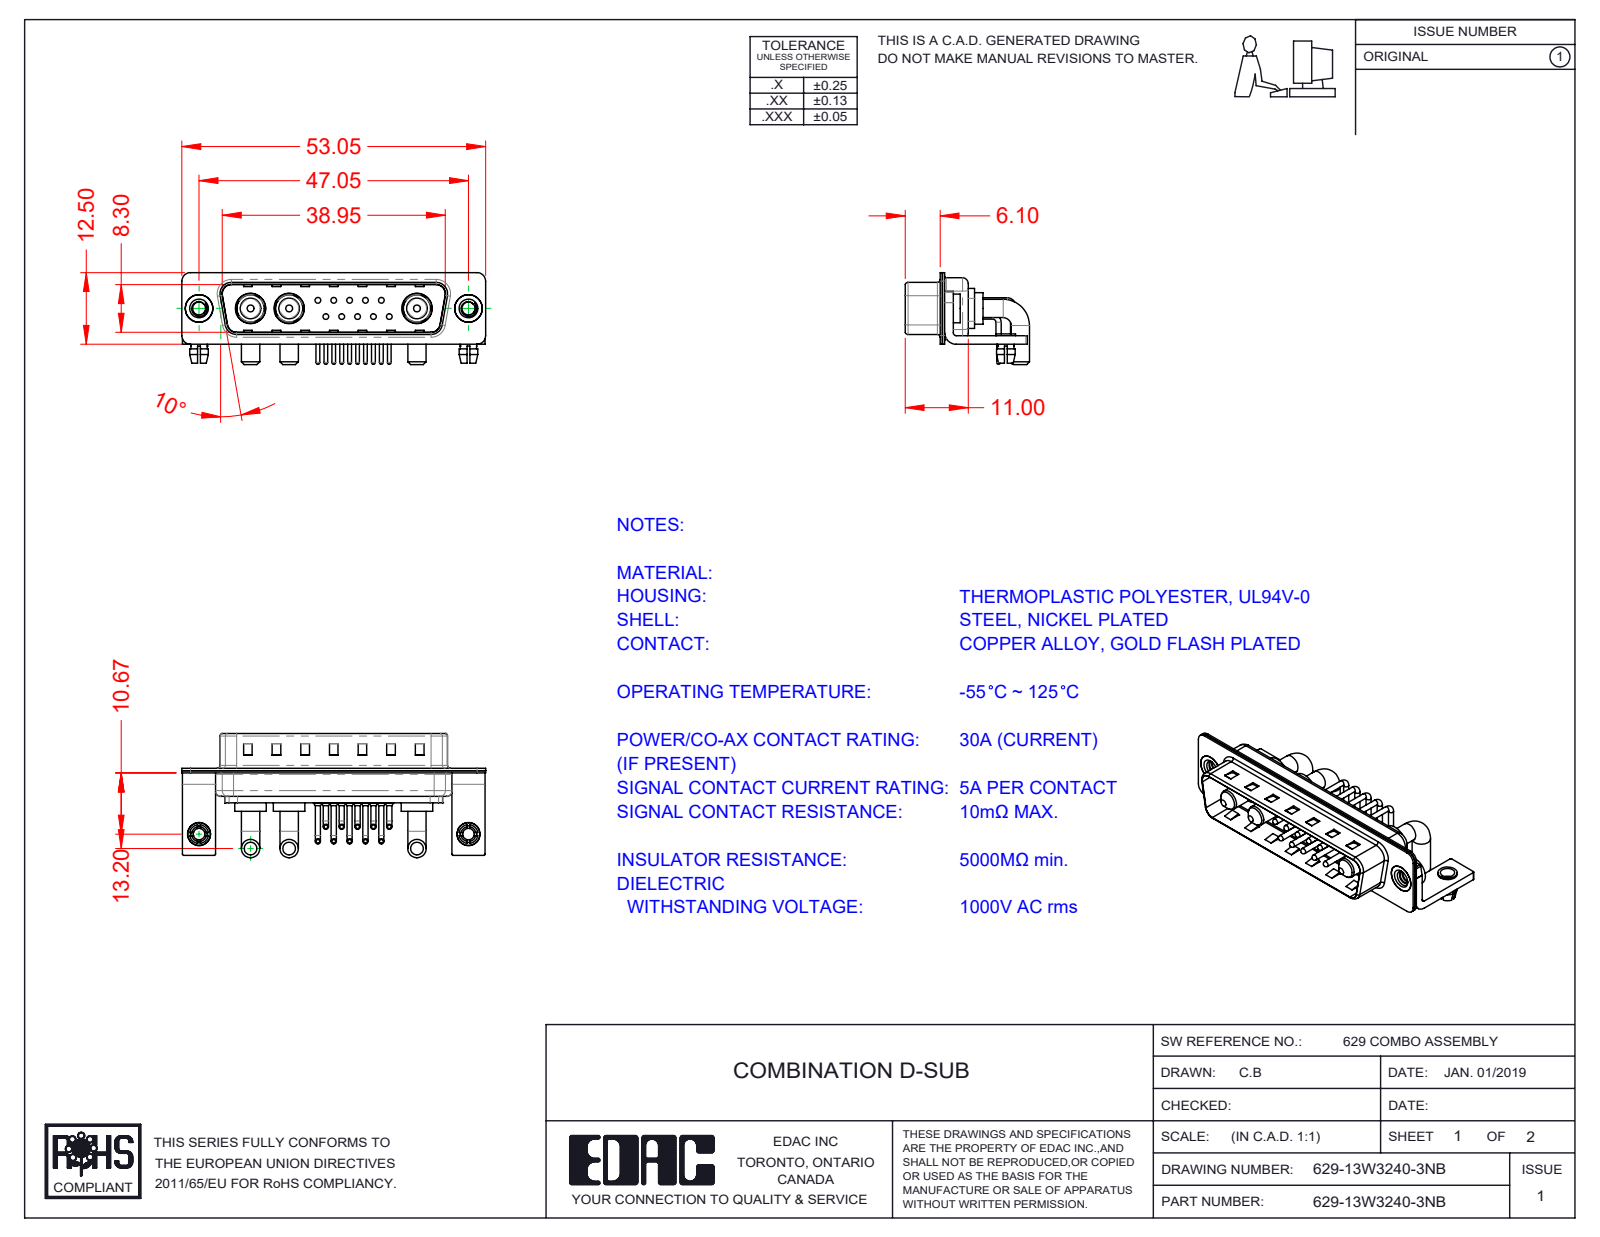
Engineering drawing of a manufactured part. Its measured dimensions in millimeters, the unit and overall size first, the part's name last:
Units: millimetres
Overall size (bounding box): 53.05 × 21.7 × 16.05
Round holes (diameter × count): ⌀2 ×12, ⌀0.75 ×10, ⌀1.6 ×10, ⌀4.85 ×3, ⌀5.3 ×3, ⌀2.26 ×2, ⌀2.5 ×2, ⌀3.2 ×2, ⌀4 ×2, ⌀4.8 ×2
Round bosses / shafts (diameter × count): ⌀0.9 ×20, ⌀1.5 ×10, ⌀1 ×10, ⌀0.65 ×10, ⌀3.2 ×6, ⌀5.5 ×3, ⌀5.2 ×3, ⌀4.75 ×3
Partial cylindrical surfaces — rounded edges, fillets, slot ends (radius × count): R0.25 ×16, R1.5 ×16, R2 ×13, R1.01 ×10, R0.5 ×9, R1.6 ×8, R0.6 ×4, R0.65 ×4
Main face-to-face distances: 0.4, 0.8, 9.5, 9.1, 1.5, 8.7, 9.9, 0.6, 1.2, 5.2
Hole centre spacings: 3.16, 2.77, 5.04, 5.54, 7.49, 5.03, 8.31, 10.11
Volume: 3 642 mm³ · Surface area: 8 279 mm²
Bodies: 25 solids, 1745 faces (909 planar, 616 cylindrical, 220 other)
Part name (STEP PRODUCT): 629Combo Stabilizer Bracket; Power Pin_30A RA; 629Combo Shell Front_25 Contacts; 629Combo Contact Row 2 (+6 more)
STEP written by: SolidWorks 2020 (CONFIG_CONTROL_DESIGN)
